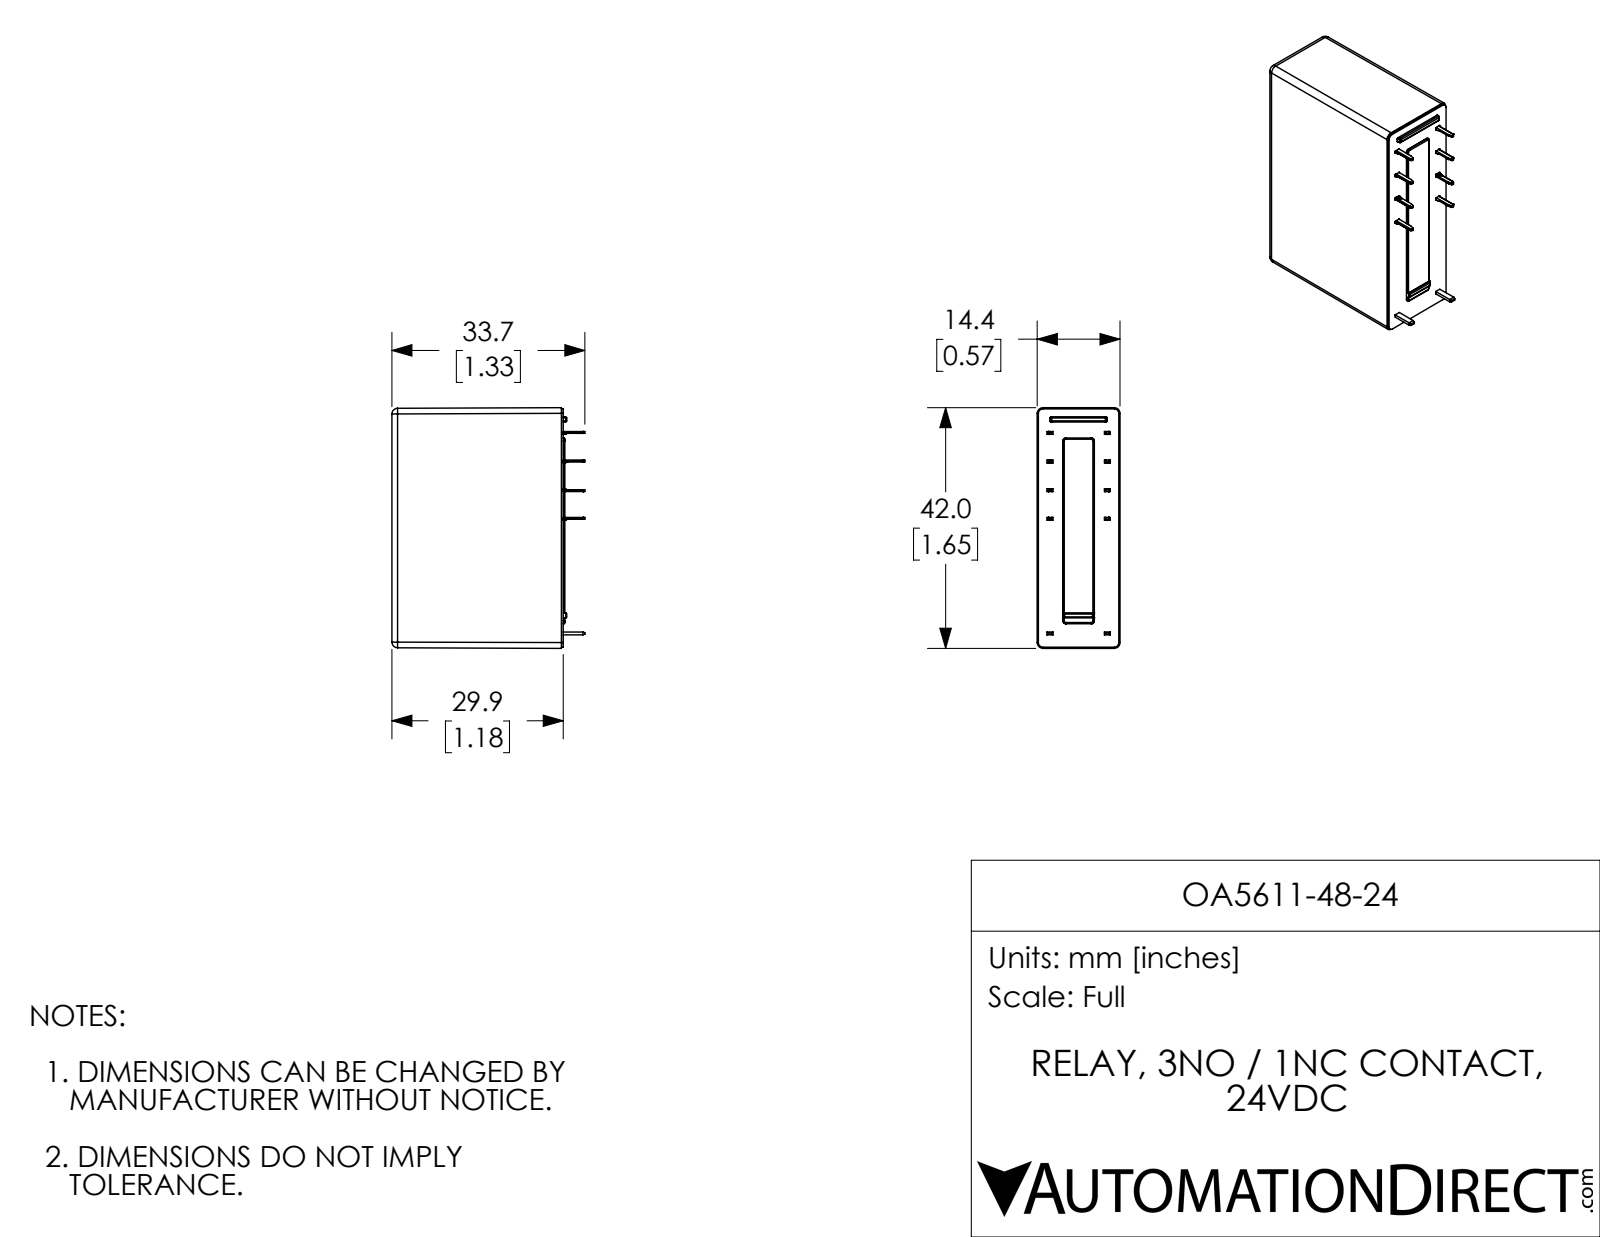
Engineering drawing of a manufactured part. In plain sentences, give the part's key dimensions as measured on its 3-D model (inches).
The part is named "OA5611-48-24". Its 3-D file was written by "SolidWorks 2017 (AUTOMOTIVE_DESIGN)". It is 1 solid with 303 faces: 173 planar, 96 cylindrical and 34 other. Overall it measures 1.653 by 1.327 by 0.569 inches. Its volume is 1.098 cubic inches and its surface area 7.115 square inches. Round bosses or shafts: 1 of diameter 0.031. Partial cylindrical surfaces (rounded edges, fillets, slot ends): 24 of radius 0.006, 16 of radius 0.008, 12 of radius 0.02, 8 of radius 0.039, 4 of radius 0.031, 2 of radius 0.005, 2 of radius 0.01. The main face-to-face distances are 1.177, 1.189, 0.024, 1.165, 0.035, 0.394, 1.201, 0.554, 0.013, 0.096.
